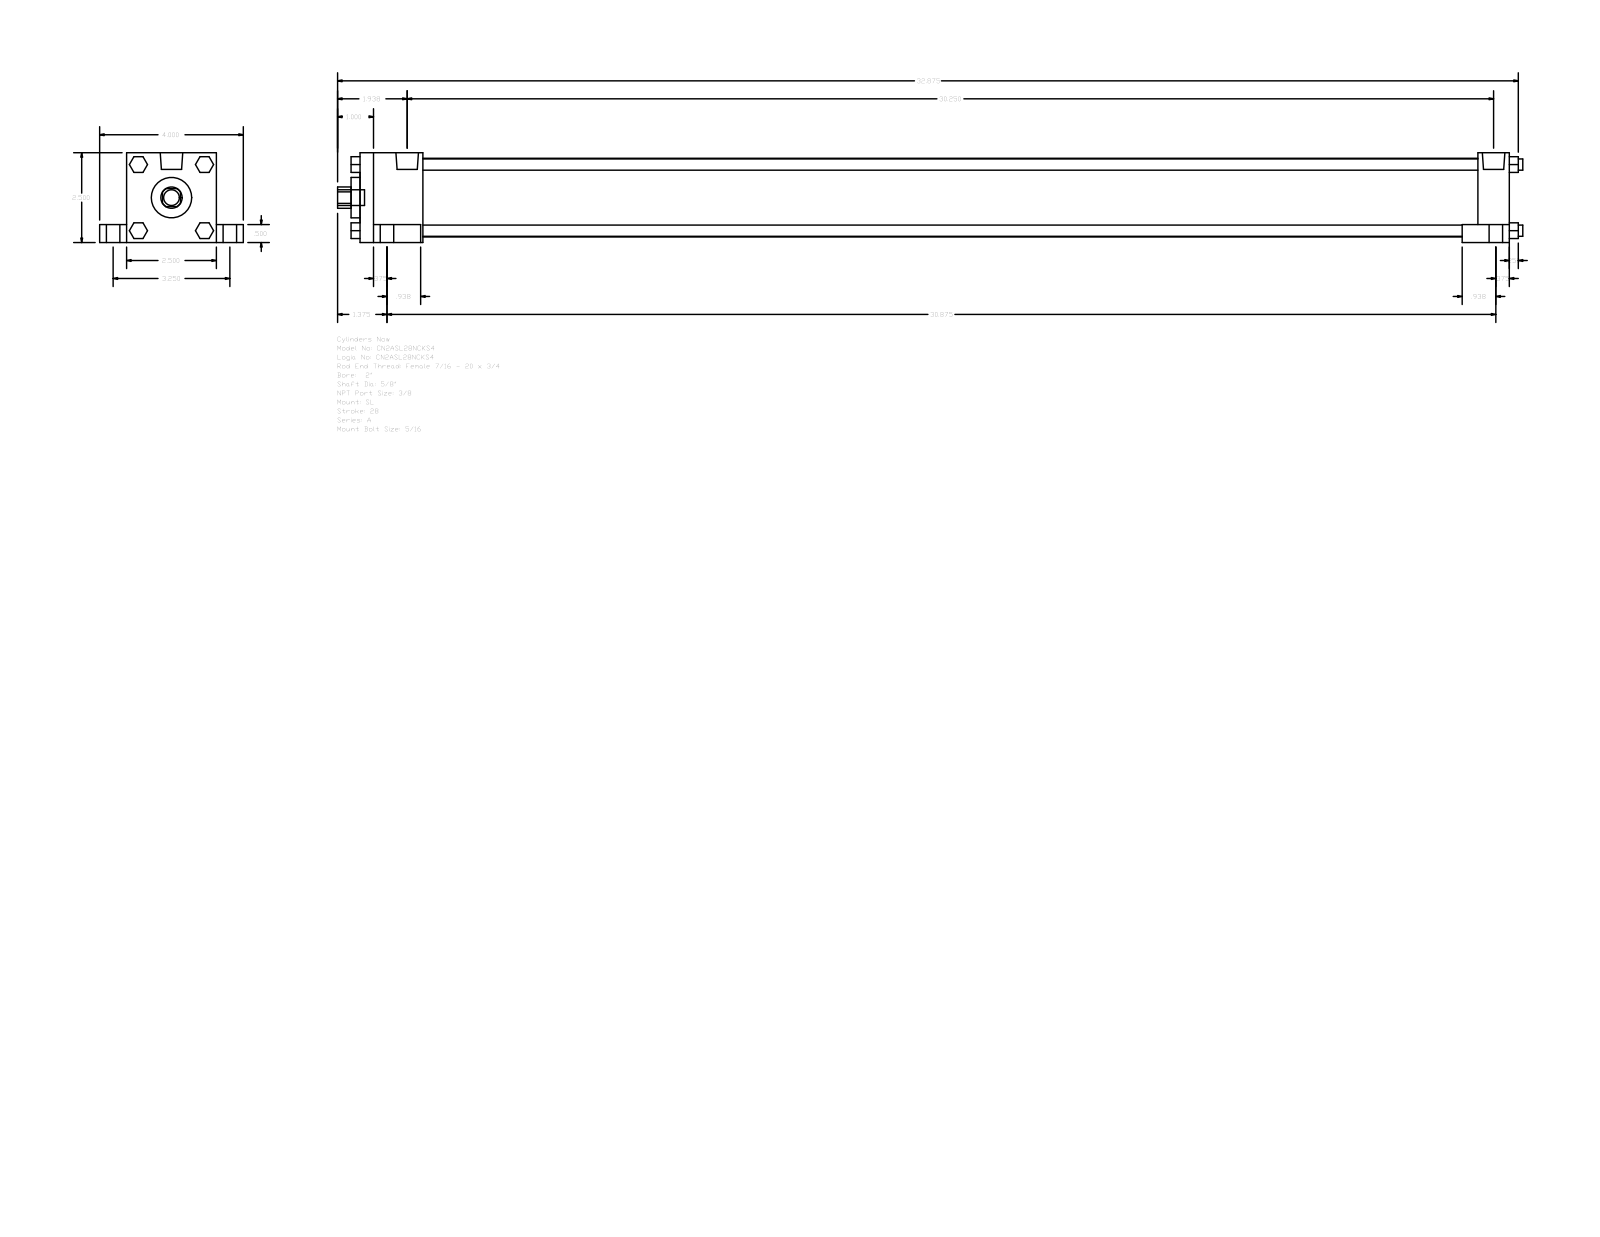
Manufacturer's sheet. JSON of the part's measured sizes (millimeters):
{"part_name": "A_SL__0200_0.625", "step_written_by": "GSSL Pune (CONFIG_CONTROL_DESIGN)", "units": "millimeters", "bodies": {"solids": 0, "faces": 148, "planar": 112, "cylindrical": 36, "other": 0}, "overall_size": [838.2, 101.6, 63.5], "round_holes": [[15.88, 1], [28.57, 1], [55.63, 1]], "round_bosses_or_shafts": [[15.88, 4], [9.53, 4], [7.94, 4], [5.56, 4], [15.93, 2], [11.11, 1]], "partial_cylinders_radius": [[7.54, 1]], "face_to_face_distances": [63.5, 812.79, 50.8, 12.7, 19.05, 82.55, 44.45, 768.34, 790.57, 746.12]}
